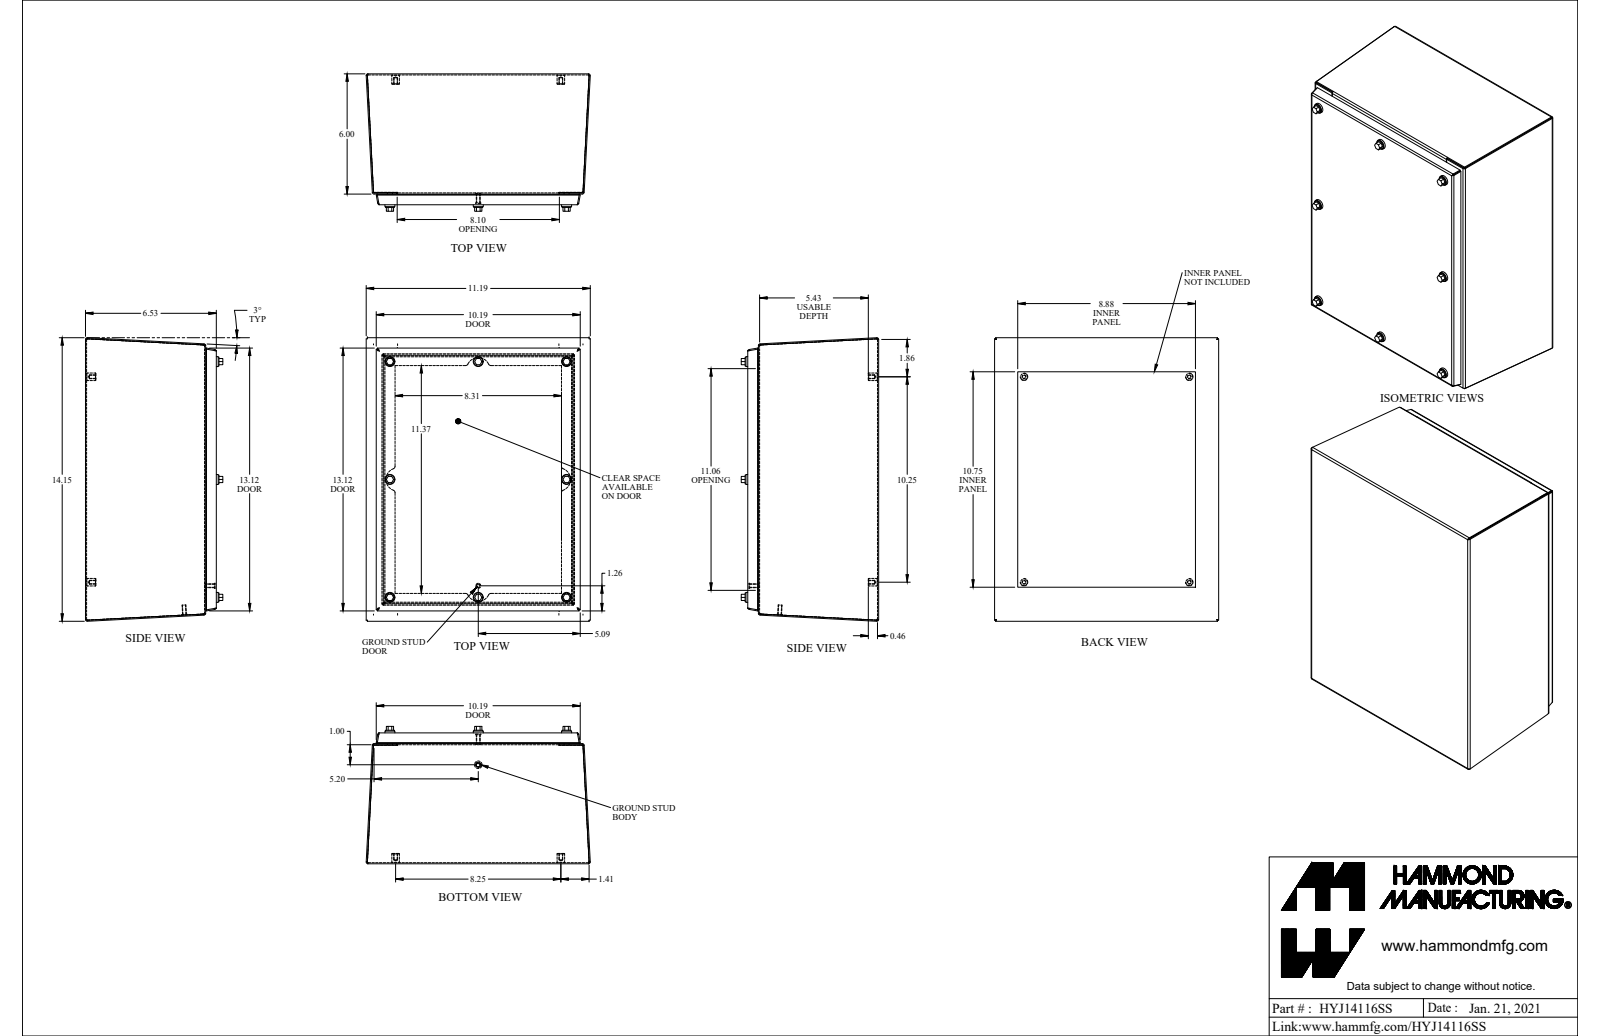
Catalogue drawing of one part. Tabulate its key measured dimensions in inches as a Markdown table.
| quantity | value |
| --- | --- |
| part name | HYJ14116SS |
| STEP written by | SolidWorks 2021 (AUTOMOTIVE_DESIGN) |
| units | inches |
| bodies | 42 solids, 657 faces (417 planar, 204 cylindrical, 36 other) |
| overall size | 14.15 × 11.186 × 6.859 |
| volume | 46.02 in³ |
| surface area | 1 515 in² |
| round holes (diameter × count) | 0.065 × 8, 0.235 × 8, 0.239 × 8, 0.24 × 8, 0.25 × 8, 0.253 × 8, 0.156 × 4, 0.4 × 4 |
| round bosses / shafts (diameter × count) | 0.375 × 12, 0.19 × 10, 0.5 × 8, 0.45 × 8, 0.406 × 8, 0.315 × 8, 0.25 × 2 |
| partial cylindrical surfaces (radius × count) | 0.029 × 16, 0.086 × 16, 0.076 × 8, 0.125 × 8, 0.055 × 4, 0.5 × 4, 0.575 × 4 |
| main face-to-face distances | 0.057, 6.418, 6.475, 6.475, 0.057, 6.532, 5.943, 0.475, 0.532, 6 |
| hole center spacings | 11.764, 0.808, 5.882, 11.011, 12.563, 13.928, 14.702, 4.194 |
